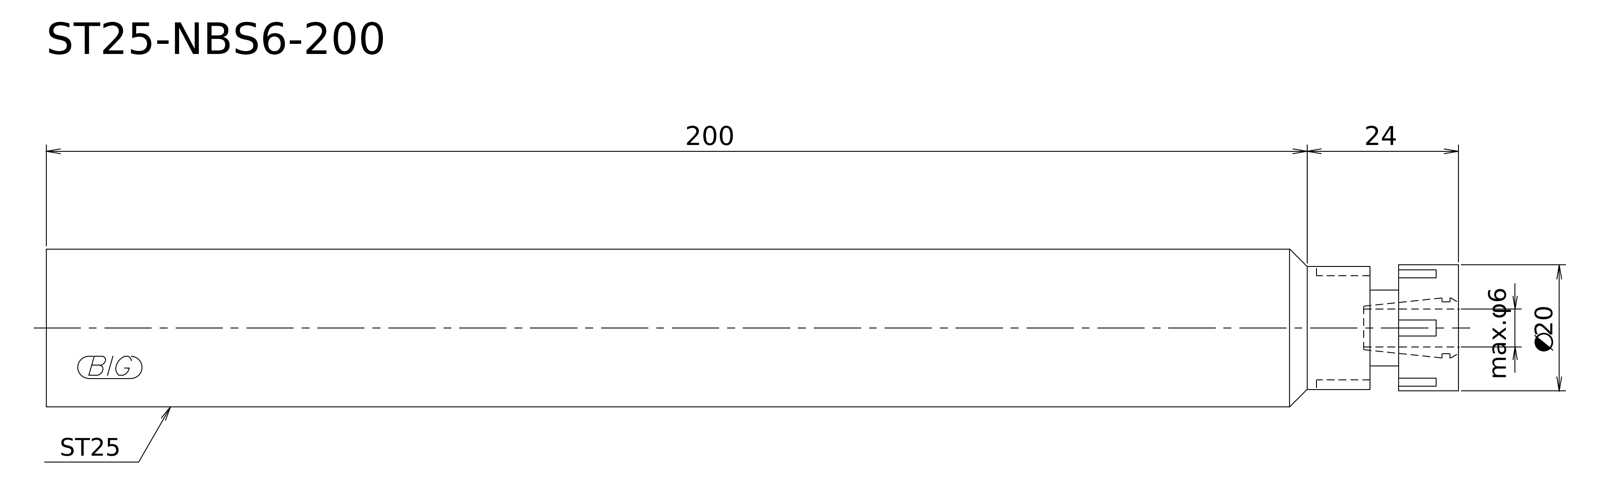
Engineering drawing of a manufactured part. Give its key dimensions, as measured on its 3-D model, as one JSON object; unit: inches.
{"step_written_by": "Kubotek KeyCreator V8.5.1 (14335) (CONFIG_CONTROL_DESIGN)", "units": "inches", "bodies": {"solids": 1, "faces": 9, "planar": 4, "cylindrical": 4, "other": 1}, "overall_size": [8.819, 0.984, 0.984], "volume_in3": 6.37, "surface_area_in2": 28.42, "round_bosses_or_shafts": [[0.984, 1], [0.787, 1], [0.768, 1], [0.472, 1]], "face_to_face_distances": [8.819, 0.374, 8.445, 0.551, 0.177, 8.268]}
